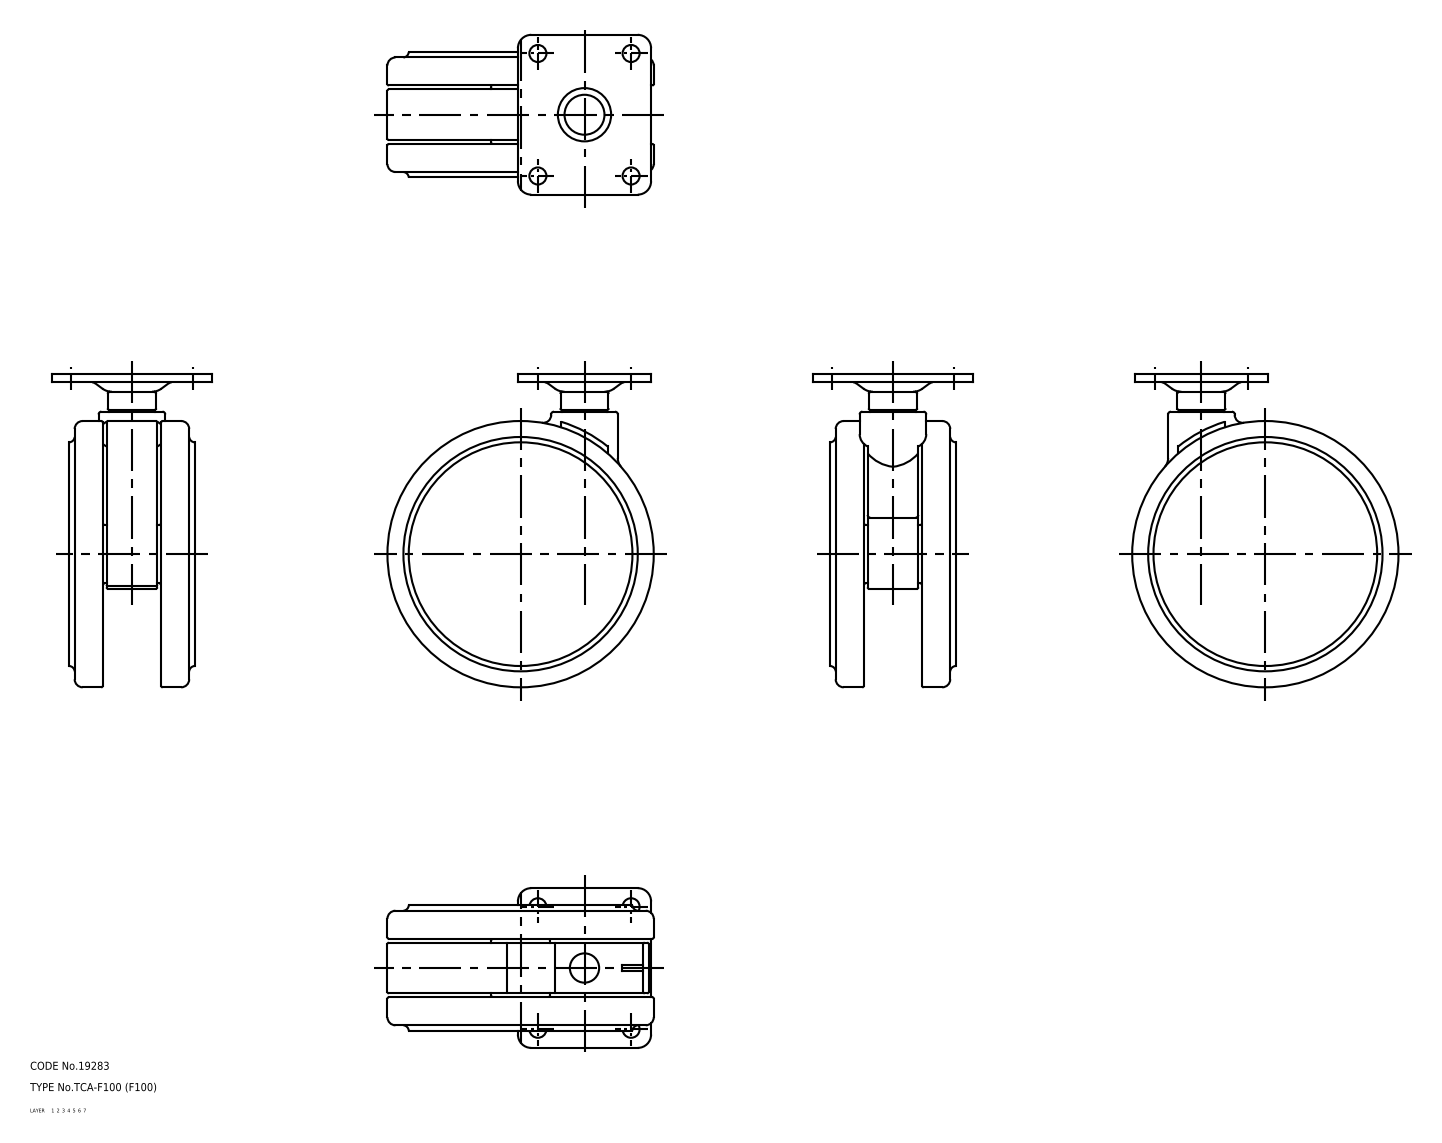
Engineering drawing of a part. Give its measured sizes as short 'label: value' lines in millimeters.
name: 67120205; 67120218; 67120231; 67120244 (+1 more)
written by: CADfix (AUTOMOTIVE_DESIGN)
unit: mm
bodies: 5 solids, 152 faces (0 planar, 0 cylindrical, 152 other)
size: 117.5 × 100 × 60
volume: 242 950 mm³; area: 63 823 mm²
